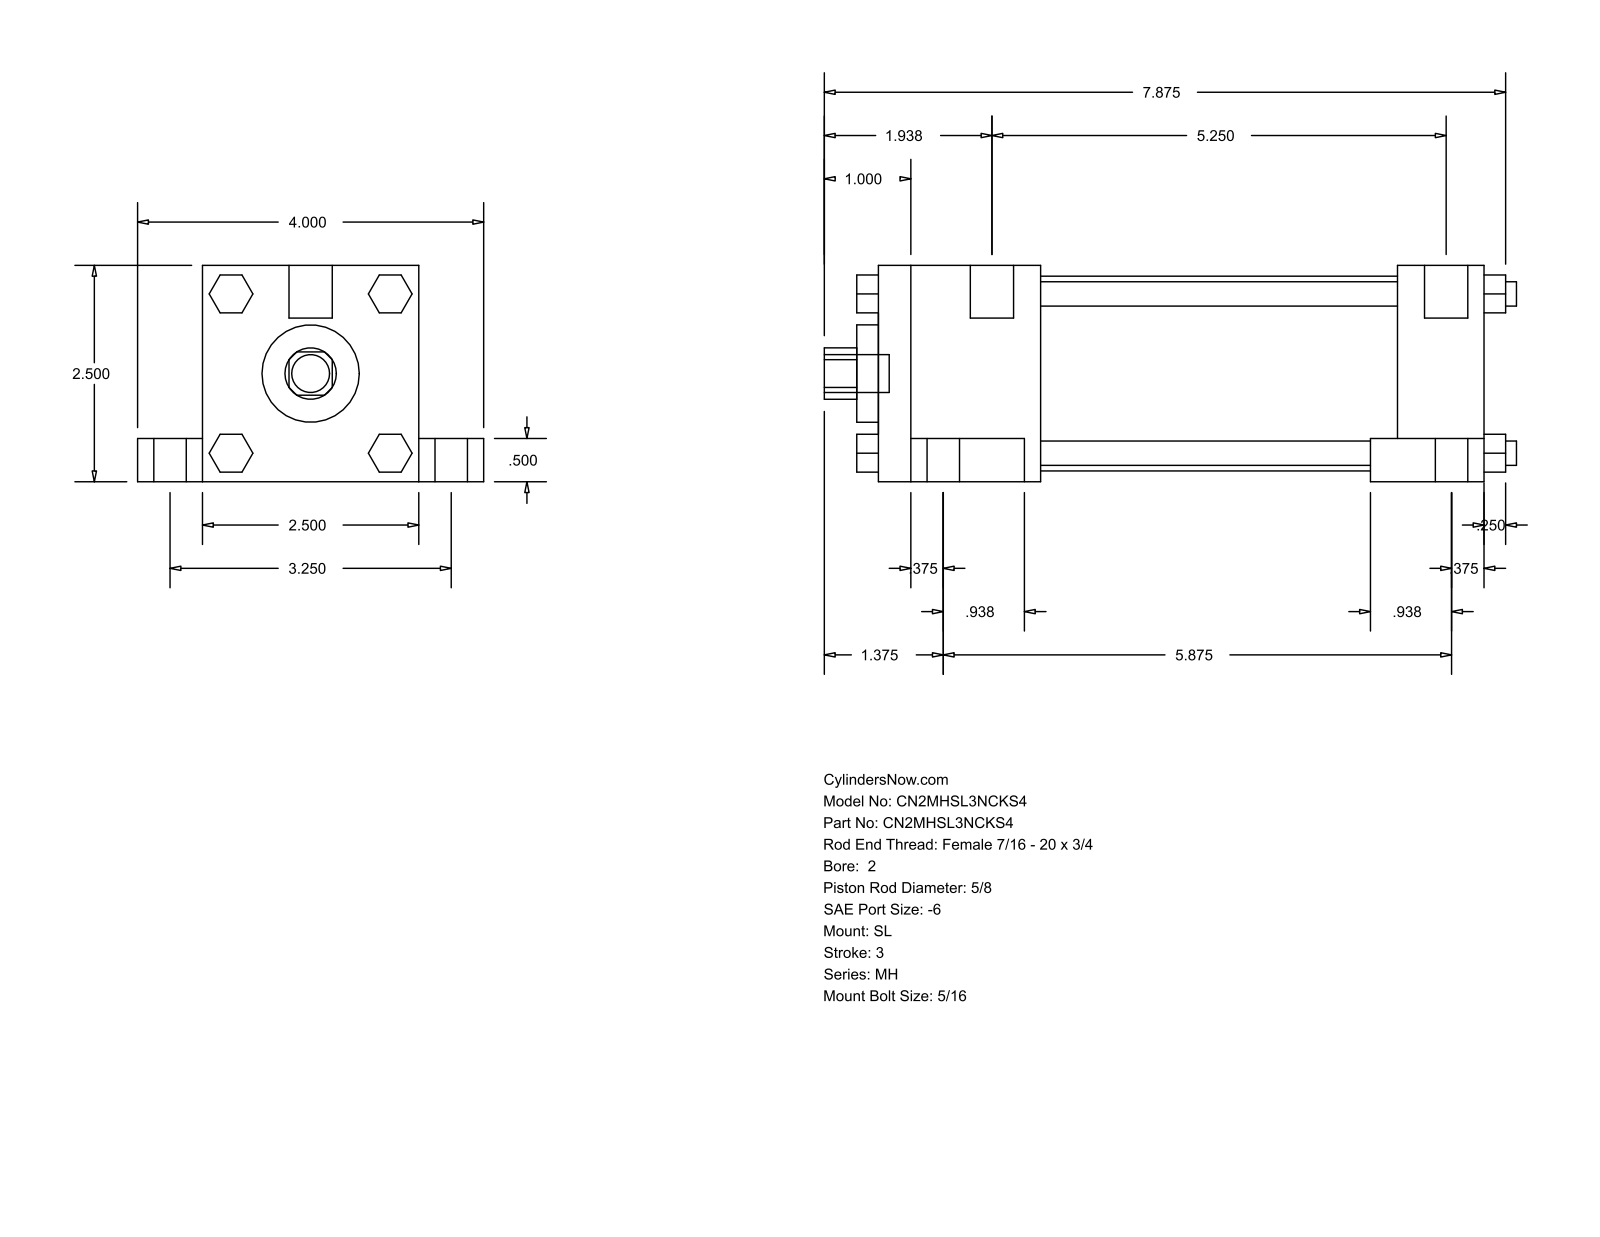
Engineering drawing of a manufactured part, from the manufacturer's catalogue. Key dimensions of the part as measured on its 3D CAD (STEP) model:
Part name (STEP PRODUCT): MH_SL__0200_0.625
STEP written by: GSSL Pune (CONFIG_CONTROL_DESIGN)
Units: millimetres
Bodies: 0 solids, 148 faces (112 planar, 36 cylindrical, 0 other)
Overall size (bounding box): 203.2 × 101.6 × 63.5
Round holes (diameter × count): ⌀15.88 ×1, ⌀28.57 ×1, ⌀57.15 ×1
Round bosses / shafts (diameter × count): ⌀15.88 ×4, ⌀9.53 ×4, ⌀7.14 ×4, ⌀5.56 ×4, ⌀12.7 ×2, ⌀11.11 ×1
Partial cylindrical surfaces — rounded edges, fillets, slot ends (radius × count): R7.54 ×1
Main face-to-face distances: 63.5, 177.8, 12.7, 19.05, 50.8, 82.55, 25.4, 101.6, 152.4, 47.62
